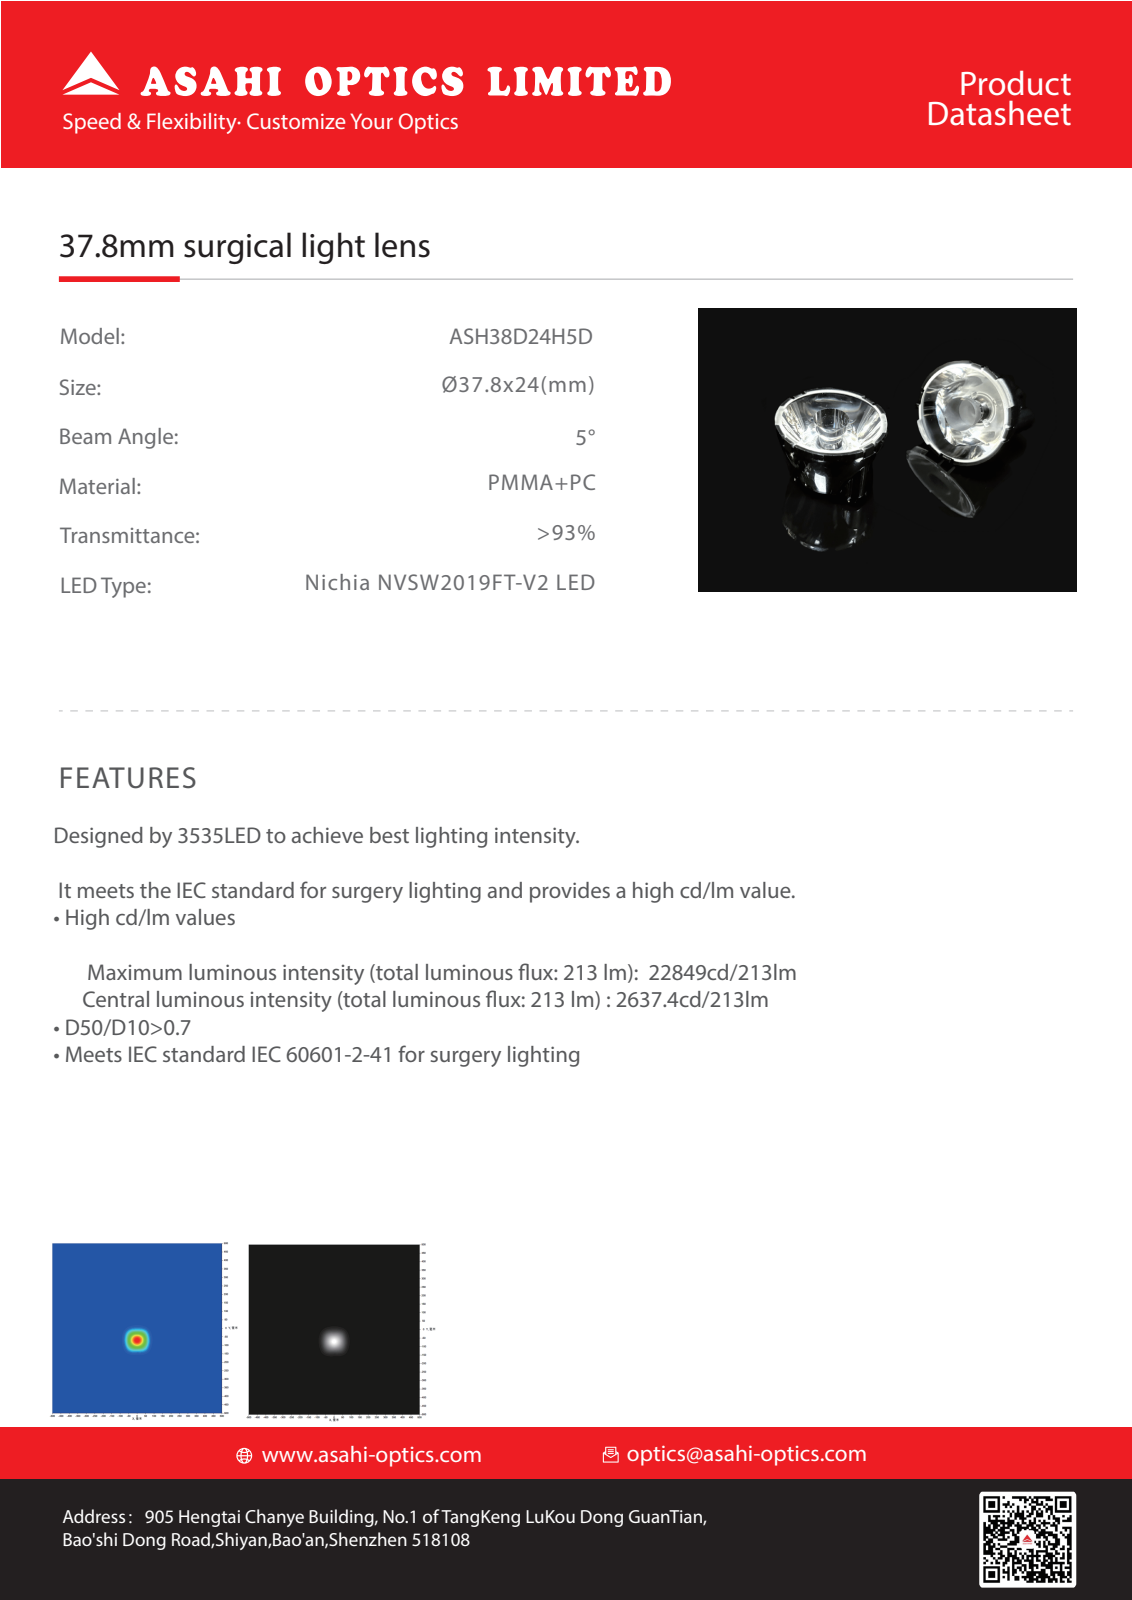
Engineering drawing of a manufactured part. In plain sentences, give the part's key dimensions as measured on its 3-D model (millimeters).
The part is named "CA16206_SURI-RS_mechanicalmodel_20170914_stp_objects". Its 3-D file was written by "SIEMENS PLM Software NX2306.9141 (AUTOMOTIVE_DESIGN)". It is 3 solids with 566 faces: 132 planar, 36 cylindrical and 398 other. Overall it measures 37.8 by 37.68 by 25.4 millimeters. Its volume is 14 934 cubic millimeters and its surface area 9 710 square millimeters. Round holes: 1 of diameter 14.5. Round bosses or shafts: 1 of diameter 20.45. Partial cylindrical surfaces (rounded edges, fillets, slot ends): 18 of radius 0.3, 8 of radius 0.15, 4 of radius 0.27. The main face-to-face distances are 23.44, 1.2, 22.24, 0.4, 1.6, 23.84, 16.65, 16.25, 15.05, 7.19.
